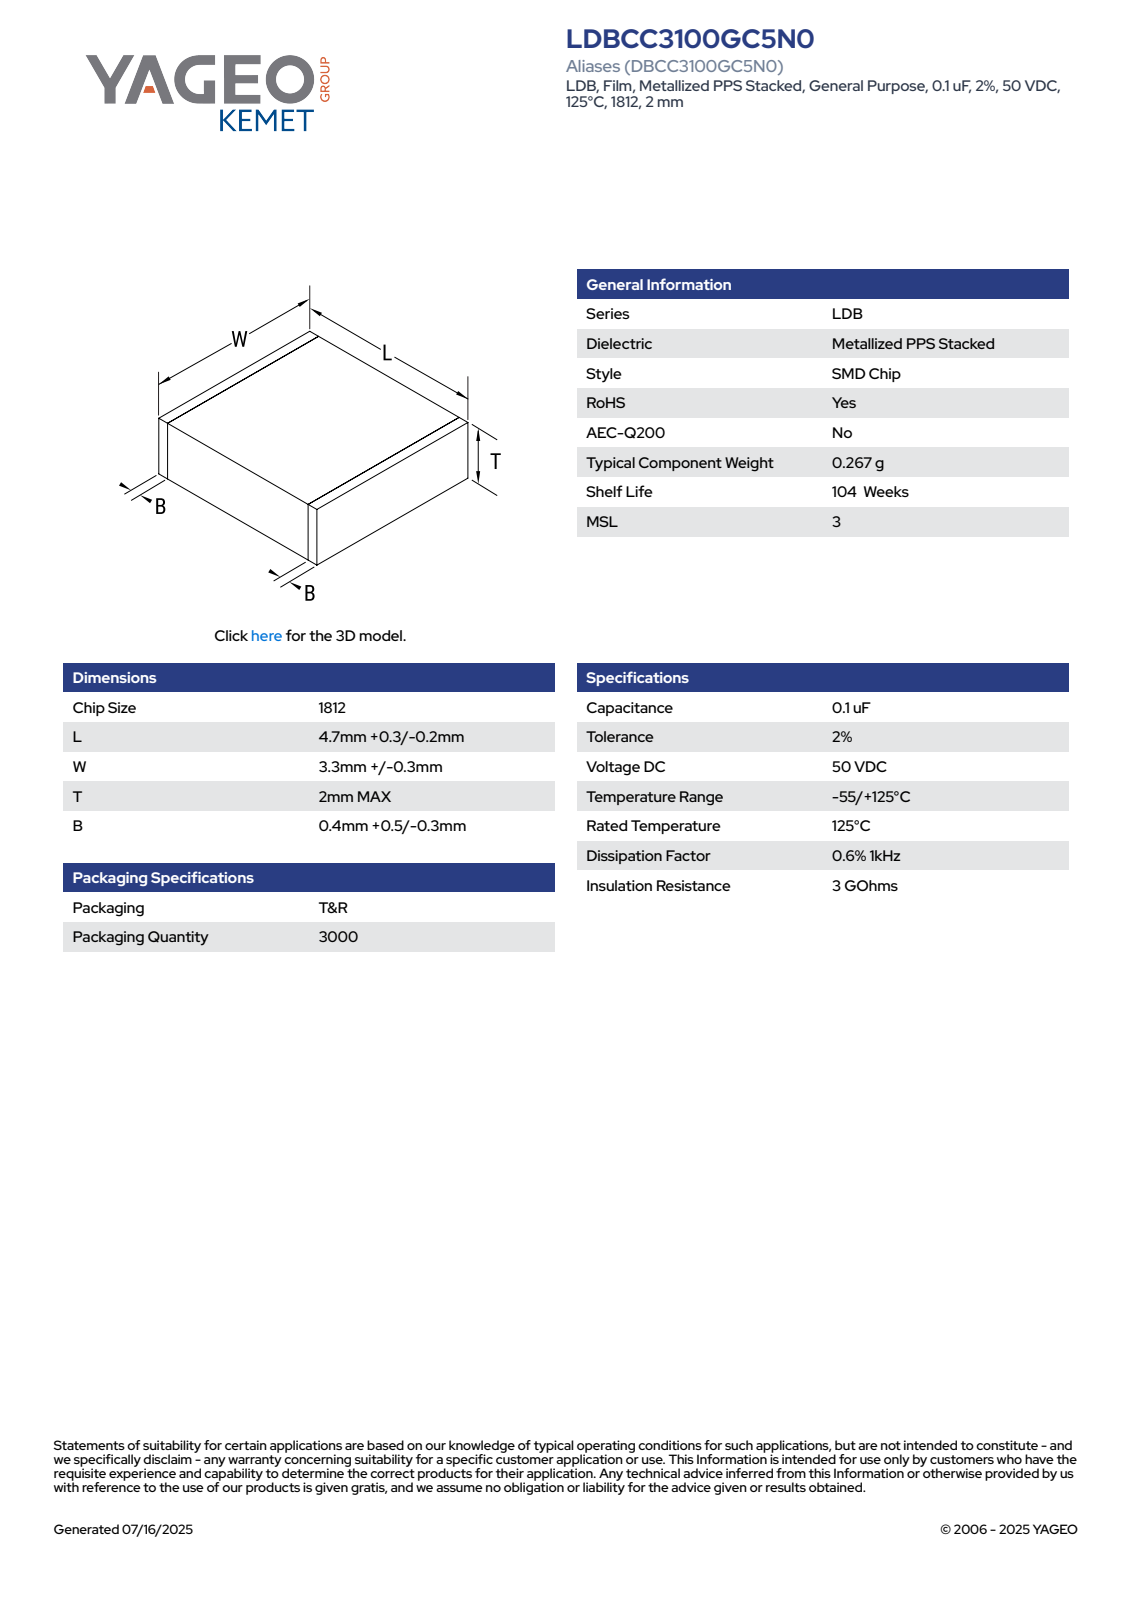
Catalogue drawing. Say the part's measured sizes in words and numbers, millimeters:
The part is named "CFS_LDELDB_1812_L5W3.6T2B0.9". Its 3-D file was written by "SolidWorks 2020 (AUTOMOTIVE_DESIGN)". It is 4 solids with 73 faces: 73 planar, 0 cylindrical and 0 other. Overall it measures 5 by 3.6 by 2 millimeters. Its volume is 36 cubic millimeters and its surface area 72 square millimeters. The main face-to-face distances are 1.98, 3.58, 5, 1.99, 3.59, 2, 3.6, 0.5, 4.5, 4.
